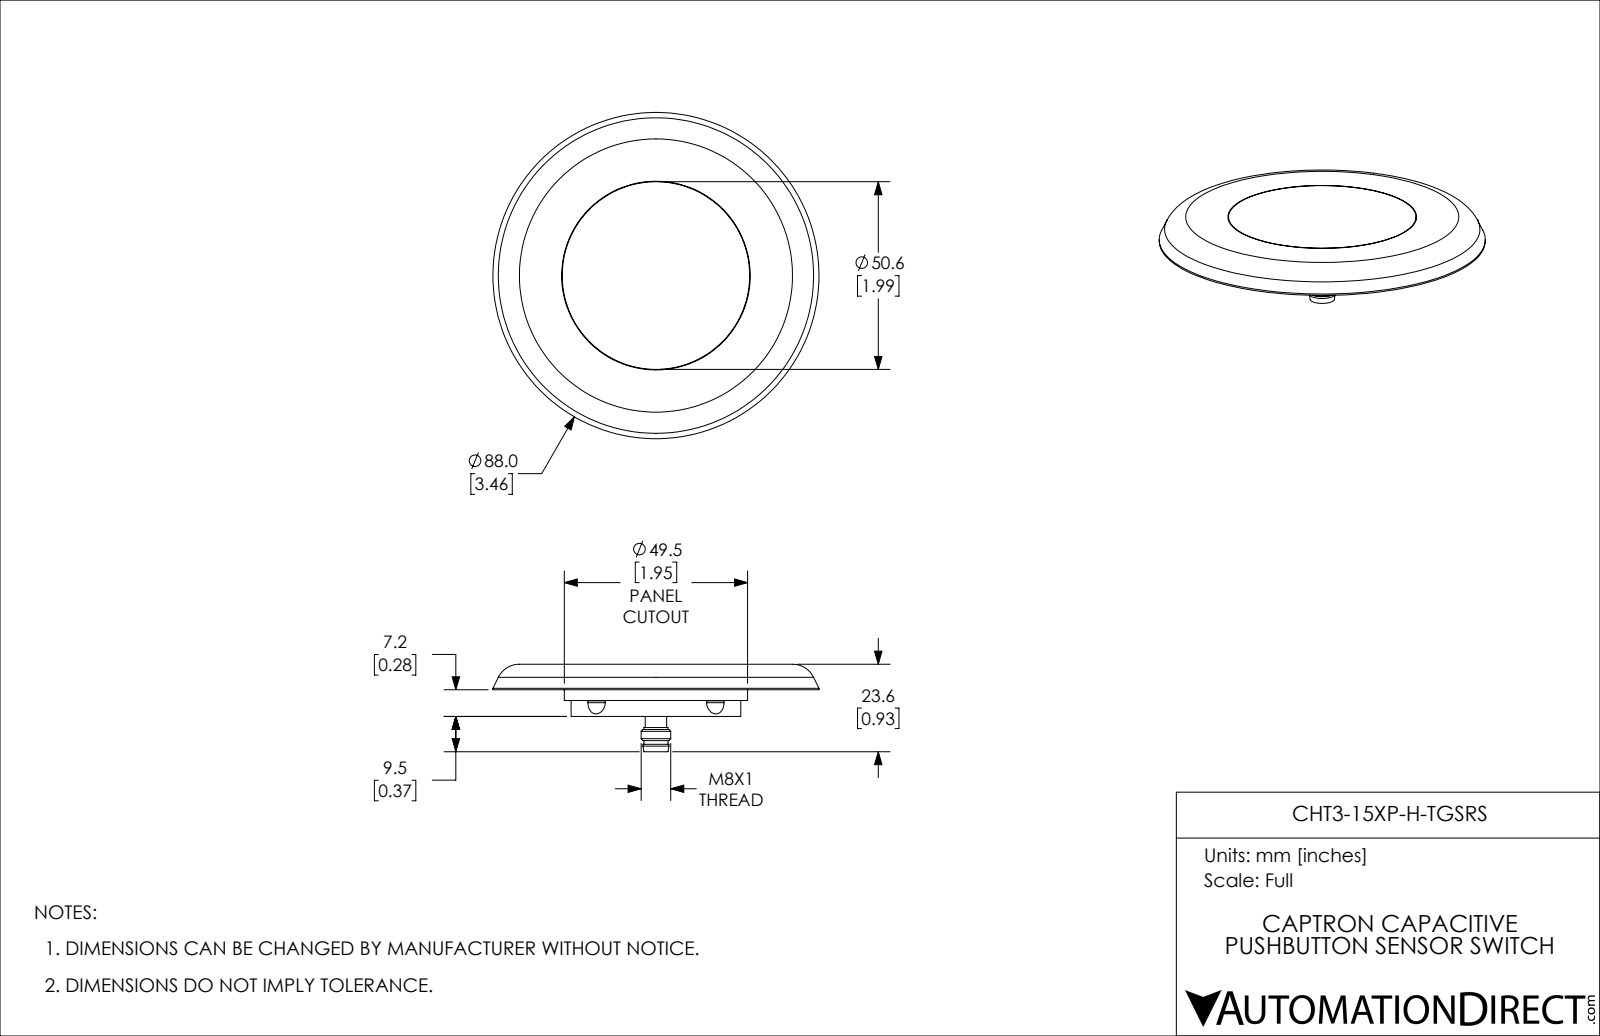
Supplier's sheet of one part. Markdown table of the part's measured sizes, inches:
| quantity | value |
| --- | --- |
| part name | CHT3-15XP-H-TGSRS |
| STEP written by | SolidWorks 2019 (CONFIG_CONTROL_DESIGN) |
| units | inches |
| bodies | 9 solids, 87 faces (25 planar, 36 cylindrical, 26 other) |
| overall size | 3.465 × 3.465 × 0.929 |
| volume | 3.031 in³ |
| surface area | 33.39 in² |
| round holes (diameter × count) | 0.236 × 1, 1.815 × 1, 2.004 × 1 |
| round bosses / shafts (diameter × count) | 0.039 × 4, 1.992 × 1, 1.948 × 1, 1.803 × 1, 0.315 × 1, 0.276 × 1, 0.256 × 1, 0.228 × 1 |
| partial cylindrical surfaces (radius × count) | 0.197 × 4, 0.035 × 1 |
| main face-to-face distances | 0.272, 0.181, 0.091, 0.283, 0.465, 0.555, 0.02, 0.295, 0.303, 0.169 |
